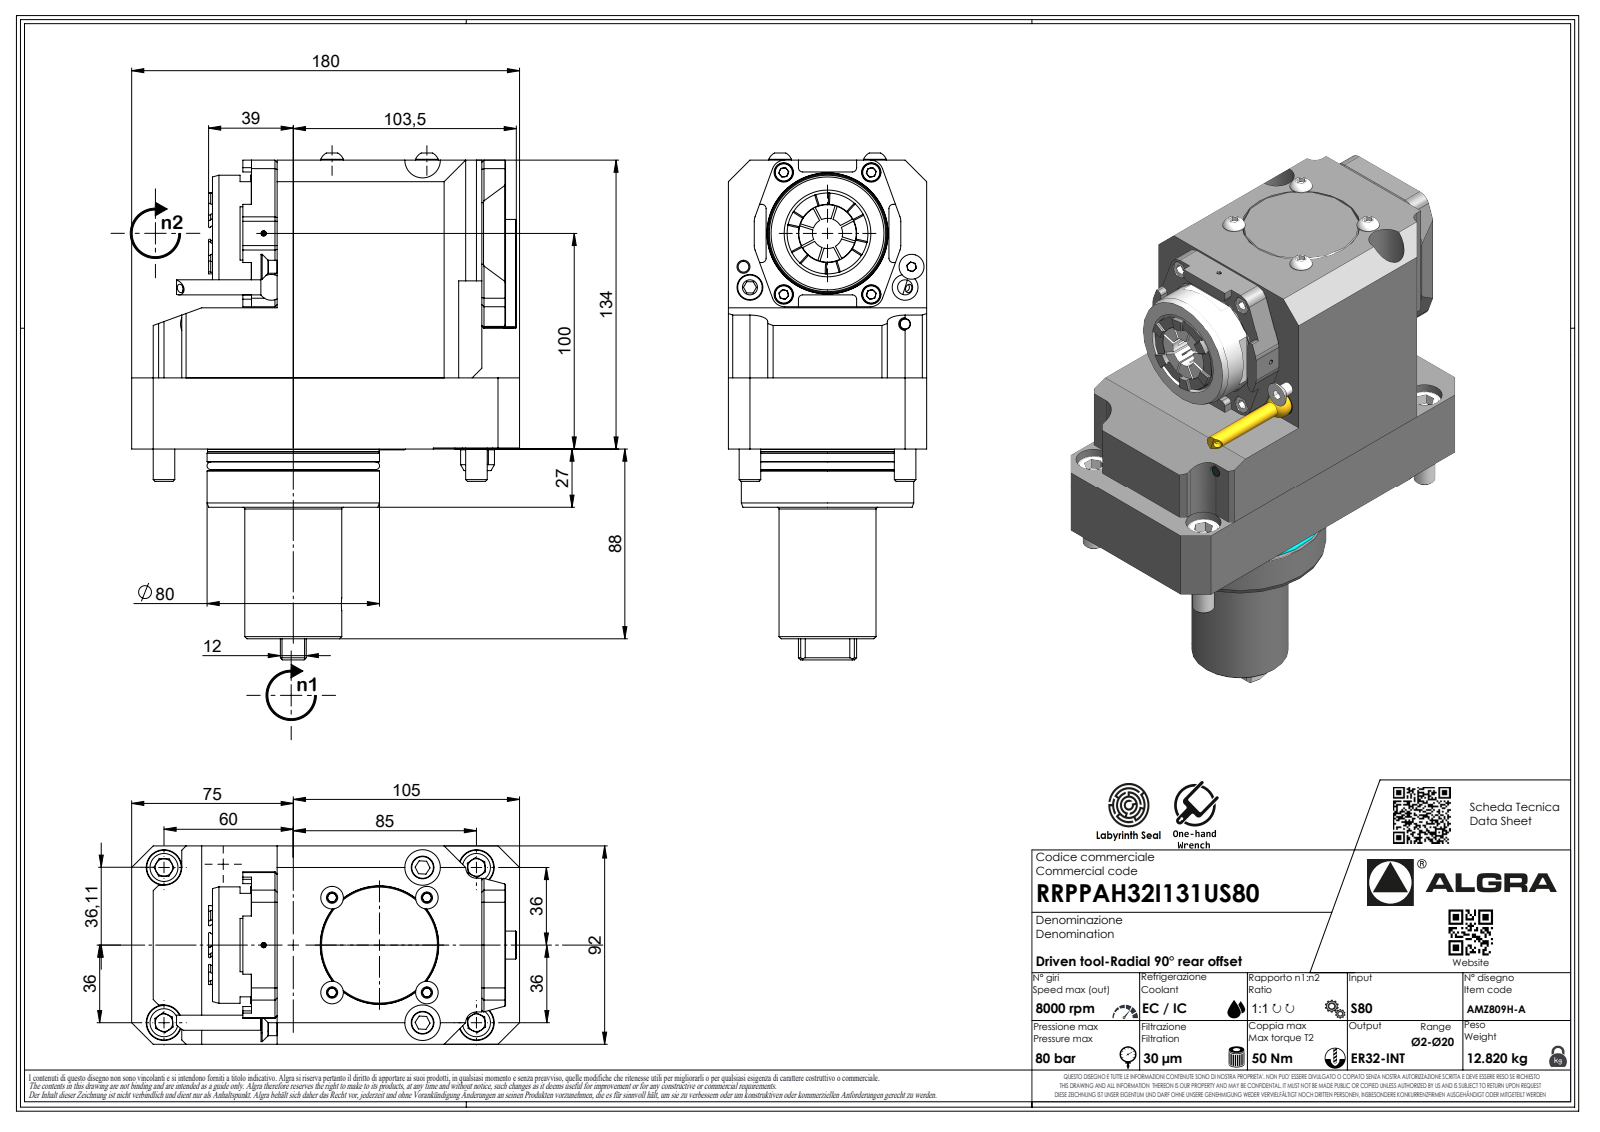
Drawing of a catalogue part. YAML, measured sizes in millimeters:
part_name: "RRPPAH32I131US80"
step_written_by: "SolidWorks 2023 (AUTOMOTIVE_DESIGN)"
units: millimeters
bodies: {solids: 1, faces: 653, planar: 392, cylindrical: 93, other: 168}
overall_size: [231.8, 180, 92]
volume: 1899000
surface_area: 123731
round_holes:
  - {diameter: 10, count: 2}
  - {diameter: 2.1, count: 1}
round_bosses_or_shafts:
  - {diameter: 10, count: 2}
  - {diameter: 80, count: 1}
  - {diameter: 79.6, count: 1}
  - {diameter: 73.6, count: 1}
  - {diameter: 54, count: 1}
  - {diameter: 45, count: 1}
  - {diameter: 6.37, count: 1}
  - {diameter: 1.7, count: 1}
partial_cylinders:
  - {radius: 2, count: 8}
  - {radius: 6, count: 8}
  - {radius: 0.33, count: 7}
  - {radius: 0.52, count: 7}
  - {radius: 3.7, count: 7}
  - {radius: 5, count: 6}
  - {radius: 8.25, count: 4}
  - {radius: 4, count: 2}
face_to_face_distances: [92, 134, 32.5, 0.5, 65.5, 33, 68.5, 27.5, 101, 27]
hole_center_spacings: [72]
